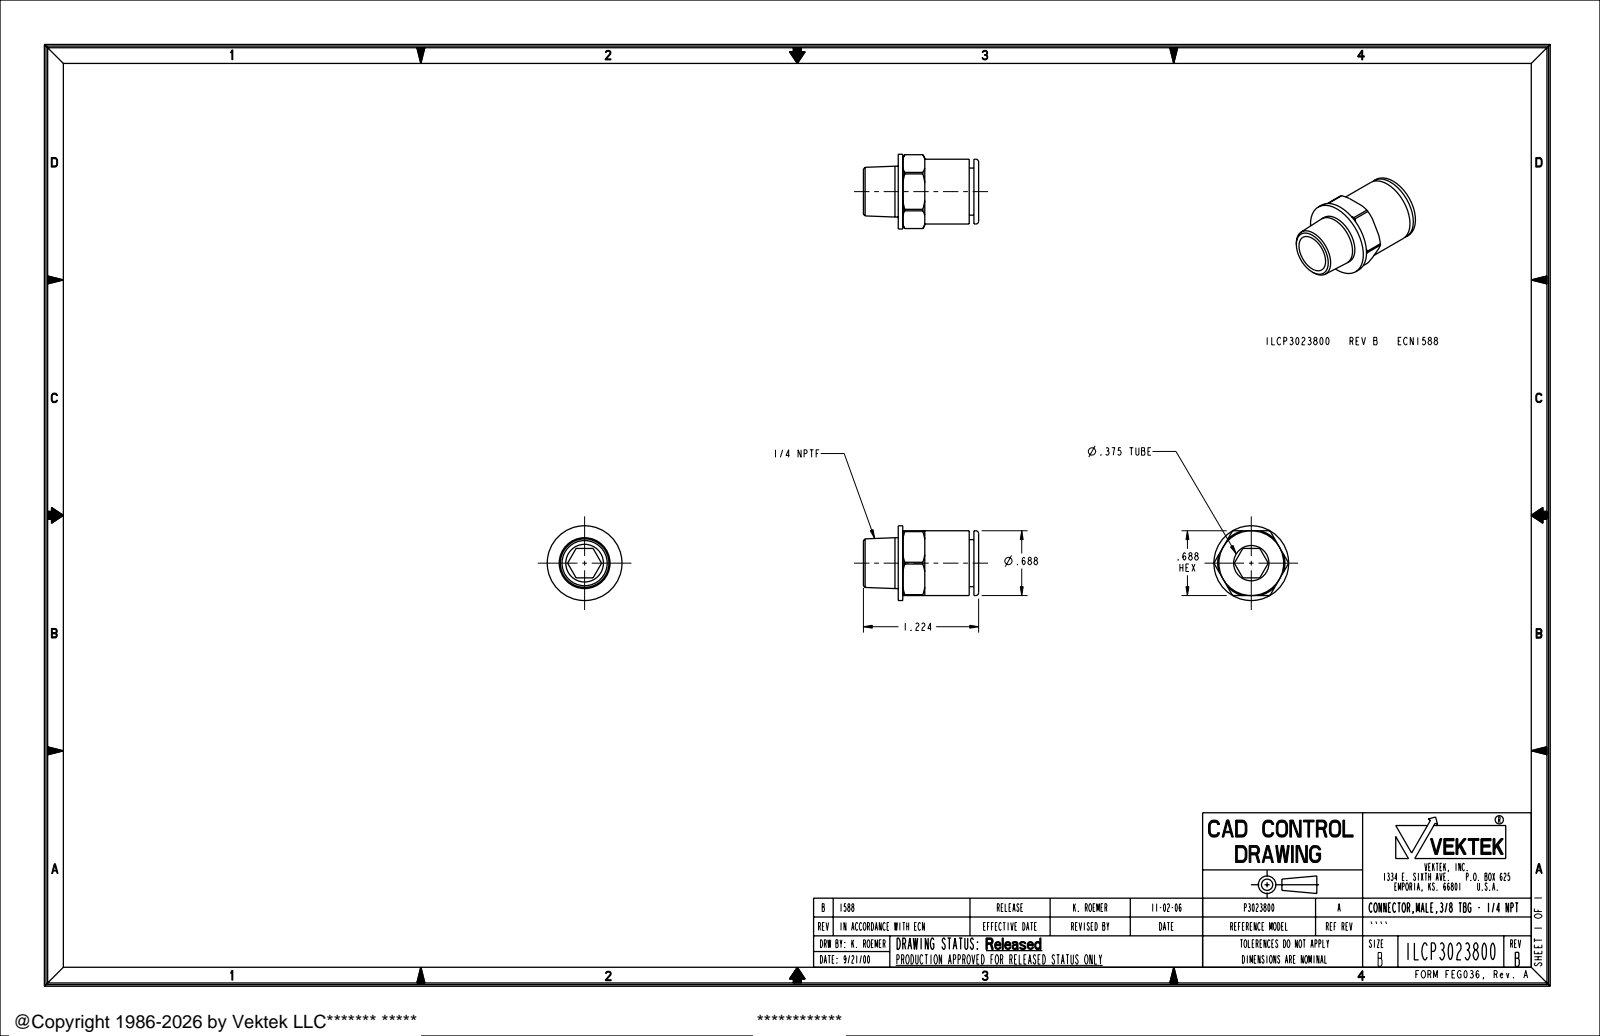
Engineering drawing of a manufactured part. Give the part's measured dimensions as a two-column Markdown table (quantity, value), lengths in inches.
| quantity | value |
| --- | --- |
| part name | ILCP3023800 |
| STEP written by | PRO/ENGINEER BY PARAMETRIC TECHNOLOGY CORPORATION, 2005180 (AUTOMOTIVE_DESIGN_CC2) |
| units | inches |
| bodies | 1 solid, 67 faces (27 planar, 22 cylindrical, 18 other) |
| overall size | 1.224 × 0.794 × 0.794 |
| volume | 0.264 in³ |
| surface area | 5.409 in² |
| round holes (diameter × count) | 0.375 × 1, 0.4 × 1 |
| round bosses / shafts (diameter × count) | 0.794 × 1, 0.688 × 1, 0.54 × 1, 0.5 × 1 |
| partial cylindrical surfaces (radius × count) | 0.392 × 1 |
| main face-to-face distances | 0.05, 0.048, 0.688, 0.806, 0.854, 0.1, 0.756, 0.804, 0.706, 0.754 |
